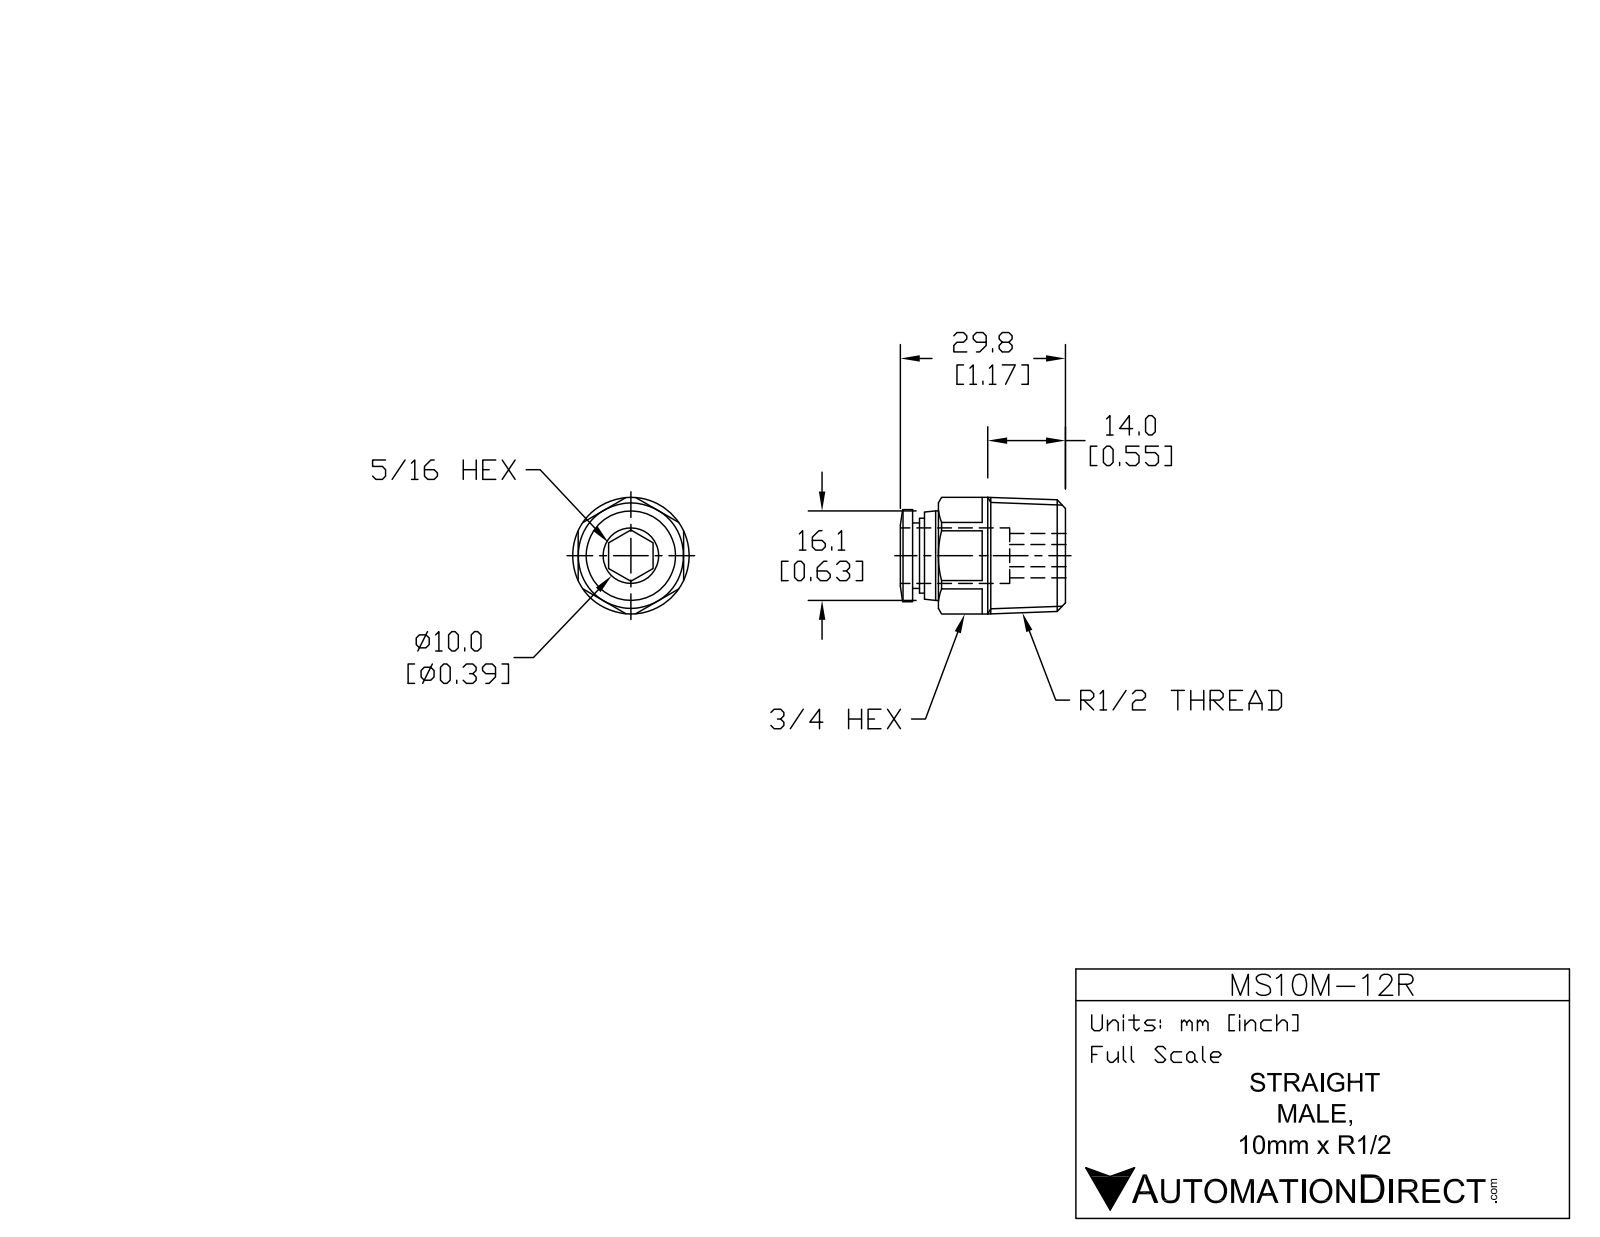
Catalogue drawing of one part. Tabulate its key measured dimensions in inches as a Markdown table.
| quantity | value |
| --- | --- |
| part name | MS10M-12R |
| STEP written by | SolidWorks 2015 (AUTOMOTIVE_DESIGN) |
| units | inches |
| bodies | 1 solid, 51 faces (19 planar, 14 cylindrical, 18 other) |
| overall size | 1.175 × 0.827 × 0.827 |
| volume | 0.395 in³ |
| surface area | 5.231 in² |
| round holes (diameter × count) | 0.315 × 1, 0.406 × 1 |
| round bosses / shafts (diameter × count) | 0.827 × 1, 0.654 × 1, 0.634 × 1, 0.531 × 1, 0.465 × 1 |
| main face-to-face distances | 0.748, 1.089, 0.906, 0.183, 1.004, 0.098, 0.085, 0.591, 0.315, 0.413 |
